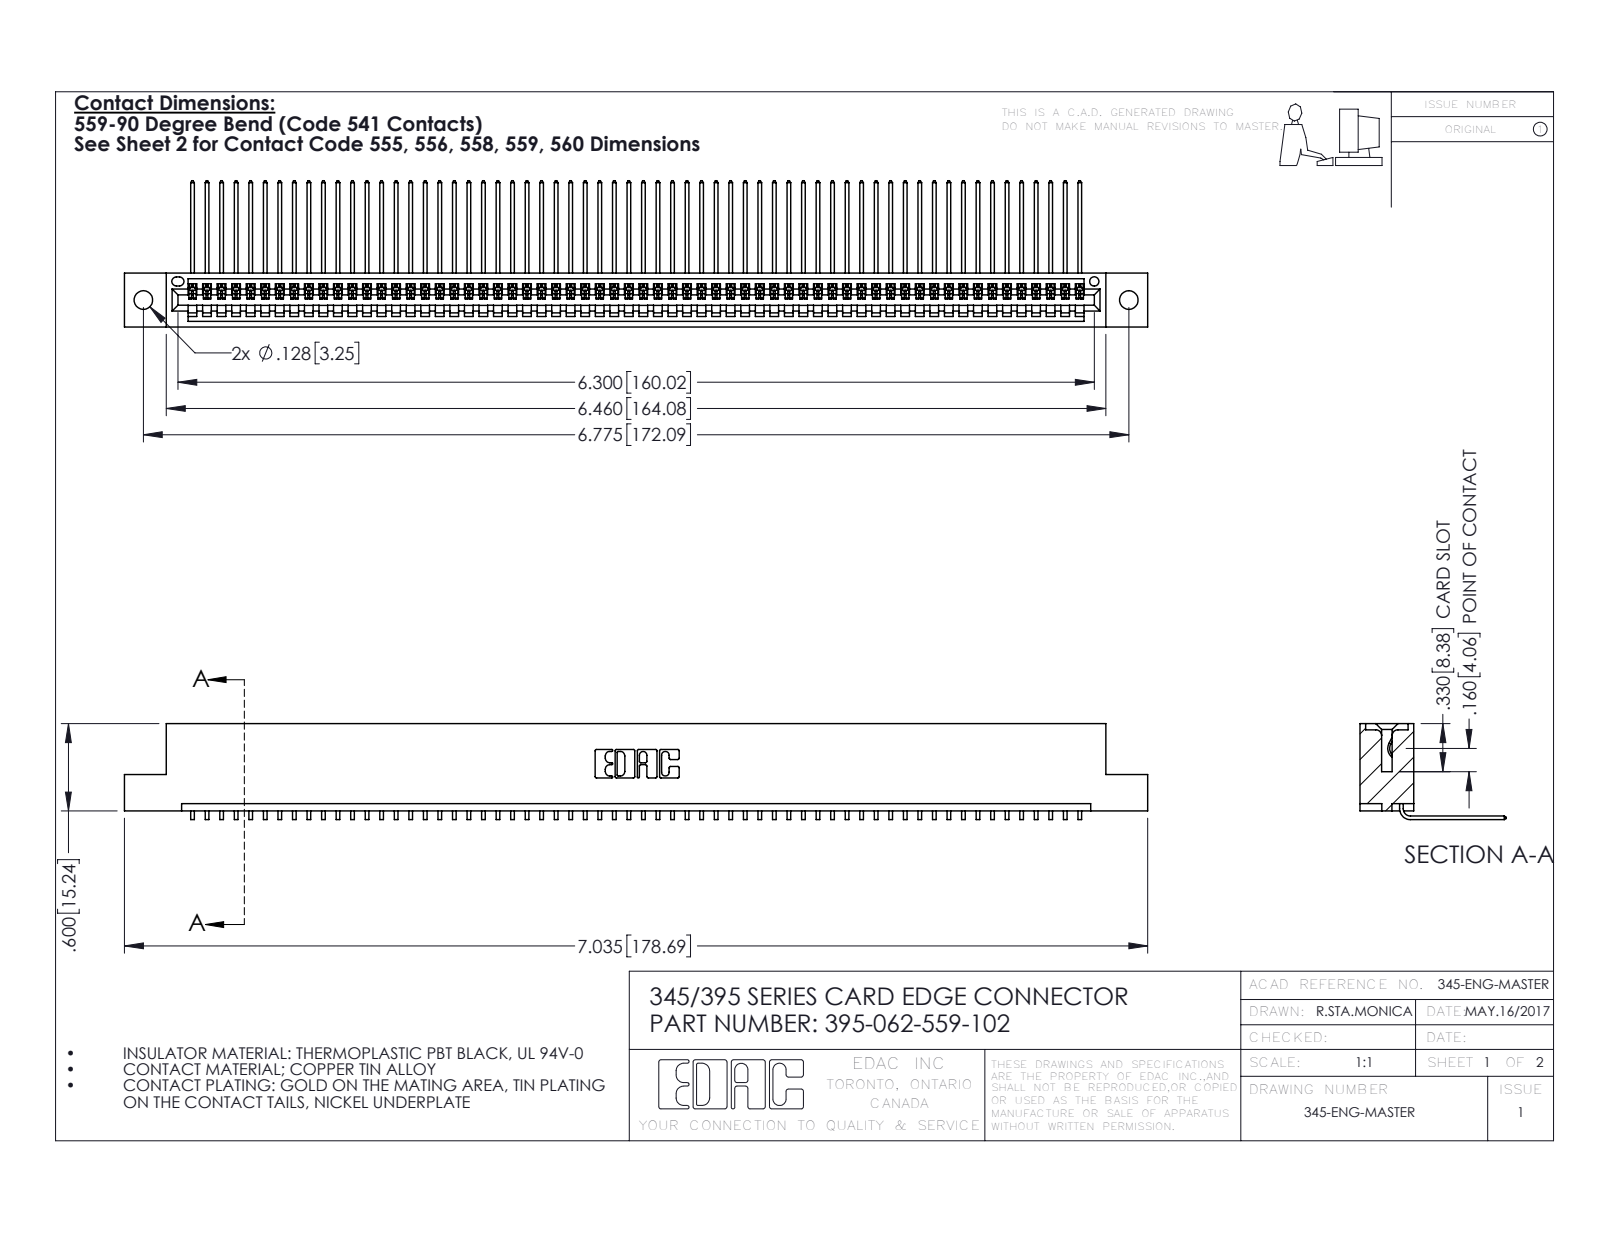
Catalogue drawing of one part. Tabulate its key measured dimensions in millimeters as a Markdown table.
| quantity | value |
| --- | --- |
| part name | 395-062-559-102; 345 Part_Flush Mounting Lugs - 0.128 Dia; 345-292-001_558 559 Tail - 1 |
| STEP written by | SolidWorks 2016 (CONFIG_CONTROL_DESIGN) |
| units | millimeters |
| bodies | 63 solids, 3846 faces (2684 planar, 1162 cylindrical, 0 other) |
| overall size | 178.7 × 25.5 × 16.7 |
| volume | 17 300 mm³ |
| surface area | 24 210 mm² |
| round holes (diameter × count) | 3.3 × 2, 1.6 × 1 |
| partial cylindrical surfaces (radius × count) | 0.2 × 124, 0.3 × 22, 0.2 × 6, 0.8 × 6, 0.7 × 3, 0.8 × 2, 1 × 2, 0.4 × 1 |
| main face-to-face distances | 7.6, 1.8, 9.4, 5.1, 2.5, 6.9, 0.6, 5.7, 3.8, 1.8 |
| hole center spacings | 6.9, 166.1, 172.1 |
